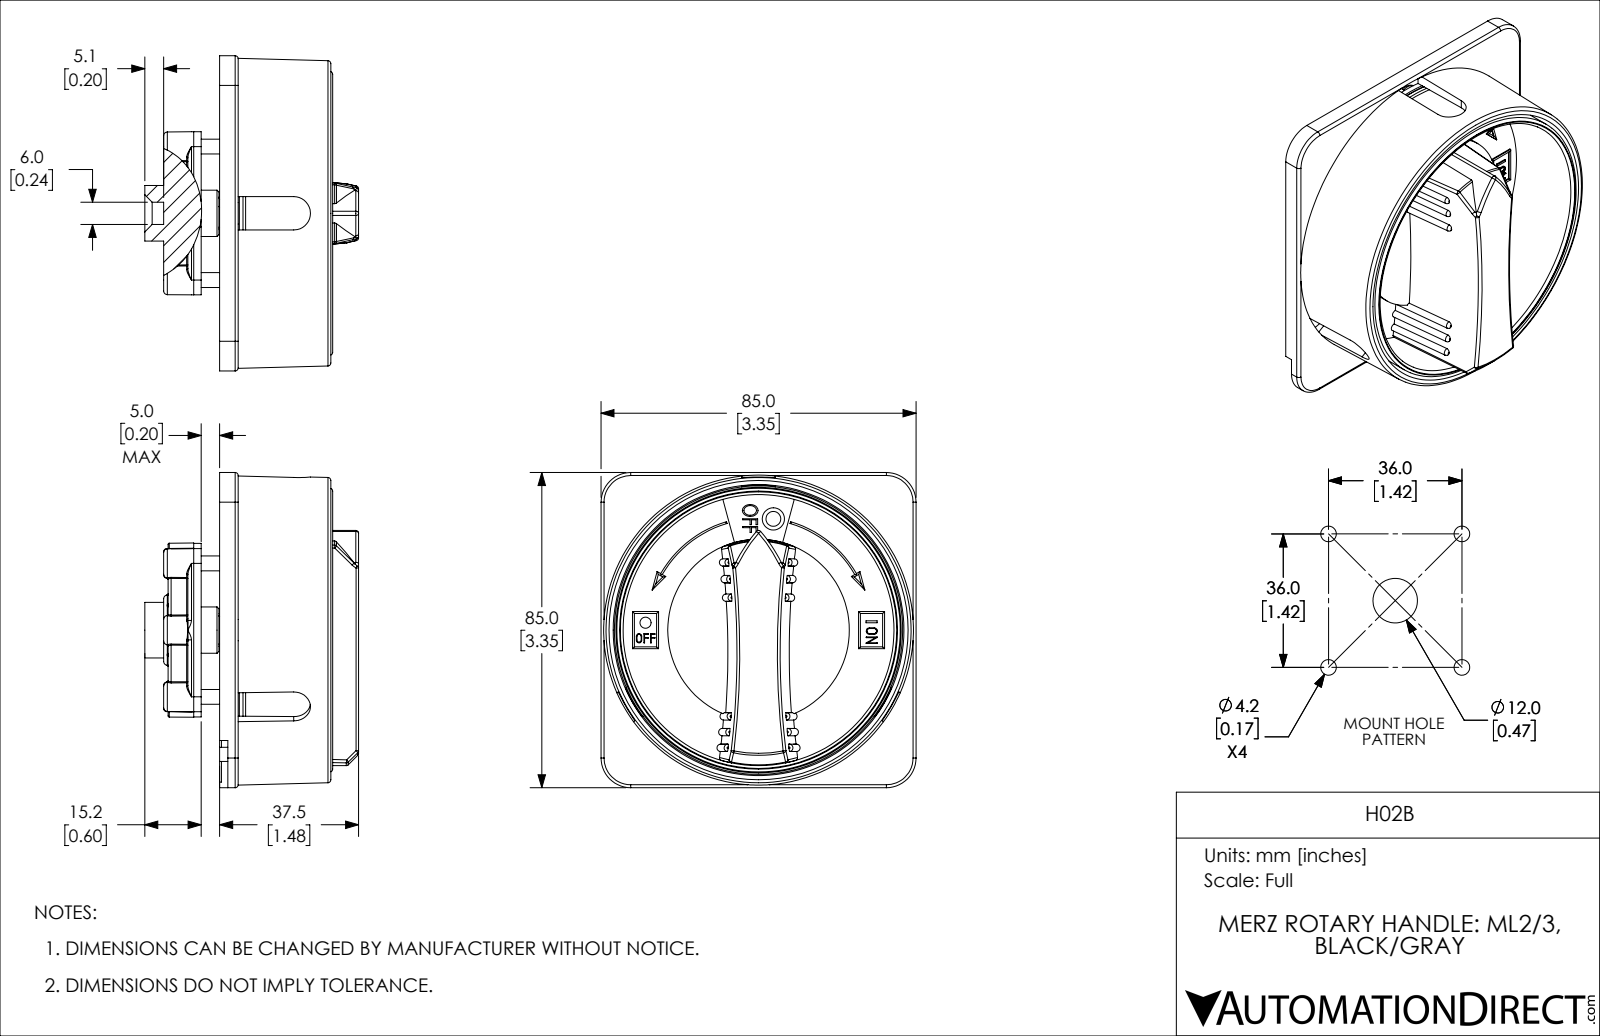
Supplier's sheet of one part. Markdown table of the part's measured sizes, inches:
| quantity | value |
| --- | --- |
| part name | H02B |
| STEP written by | SolidWorks 2019 (AUTOMOTIVE_DESIGN) |
| units | inches |
| bodies | 1 solid, 1545 faces (504 planar, 291 cylindrical, 750 other) |
| overall size | 3.346 × 3.346 × 2.272 |
| volume | 5.352 in³ |
| surface area | 103.5 in² |
| round holes (diameter × count) | 0.236 × 1, 0.807 × 1, 1.772 × 1, 2.878 × 1 |
| round bosses / shafts (diameter × count) | 0.197 × 6, 0.157 × 5, 3.031 × 1, 3.012 × 1, 1.929 × 1, 1.87 × 1, 1.024 × 1, 0.591 × 1 |
| partial cylindrical surfaces (radius × count) | 0.012 × 48, 0.031 × 24, 0.01 × 14, 0.055 × 5, 0.315 × 5, 0.039 × 4, 0.059 × 4, 0.118 × 4 |
| main face-to-face distances | 0.138, 0.079, 0.217, 0.059, 0.028, 0.11, 0.256, 0.354, 0.177, 0.335 |
| hole center spacings | 1.192 |
